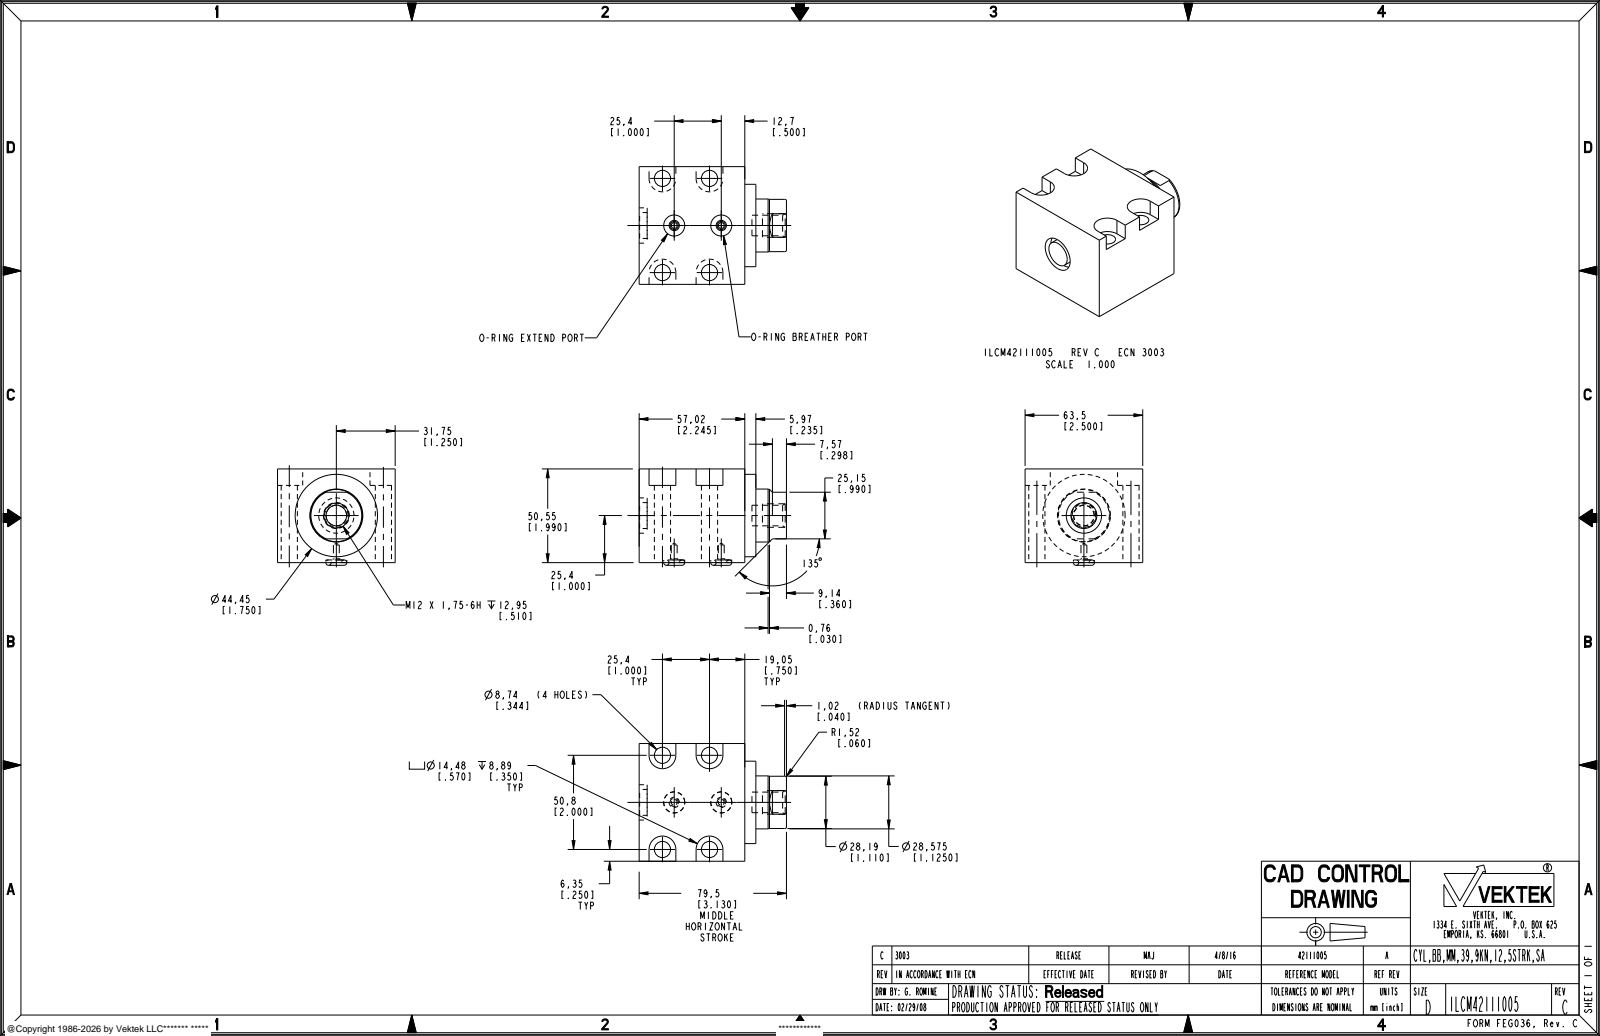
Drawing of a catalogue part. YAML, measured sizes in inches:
part_name: "ILCM42111005"
step_written_by: "PRO/ENGINEER BY PARAMETRIC TECHNOLOGY CORPORATION, 2013320 (AUTOMOTIVE_DESIGN)"
units: inches
bodies: {solids: 1, faces: 86, planar: 30, cylindrical: 34, other: 22}
overall_size: [3.13, 2.5, 2.047]
volume: 11.21
surface_area: 44.7
round_holes:
  - {diameter: 0.344, count: 4}
  - {diameter: 0.125, count: 2}
  - {diameter: 0.447, count: 2}
  - {diameter: 0.437, count: 1}
  - {diameter: 0.75, count: 1}
round_bosses_or_shafts:
  - {diameter: 1.75, count: 1}
  - {diameter: 1.125, count: 1}
  - {diameter: 1.11, count: 1}
  - {diameter: 0.55, count: 1}
  - {diameter: 0.5, count: 1}
partial_cylinders:
  - {radius: 0.285, count: 4}
face_to_face_distances: [1.99, 2.5, 2.245, 0.235, 2.48, 1.64, 0.35, 0.65, 0.885, 3.13]
hole_center_spacings: [1.031, 1, 1.25, 1.601, 2, 2.236]
